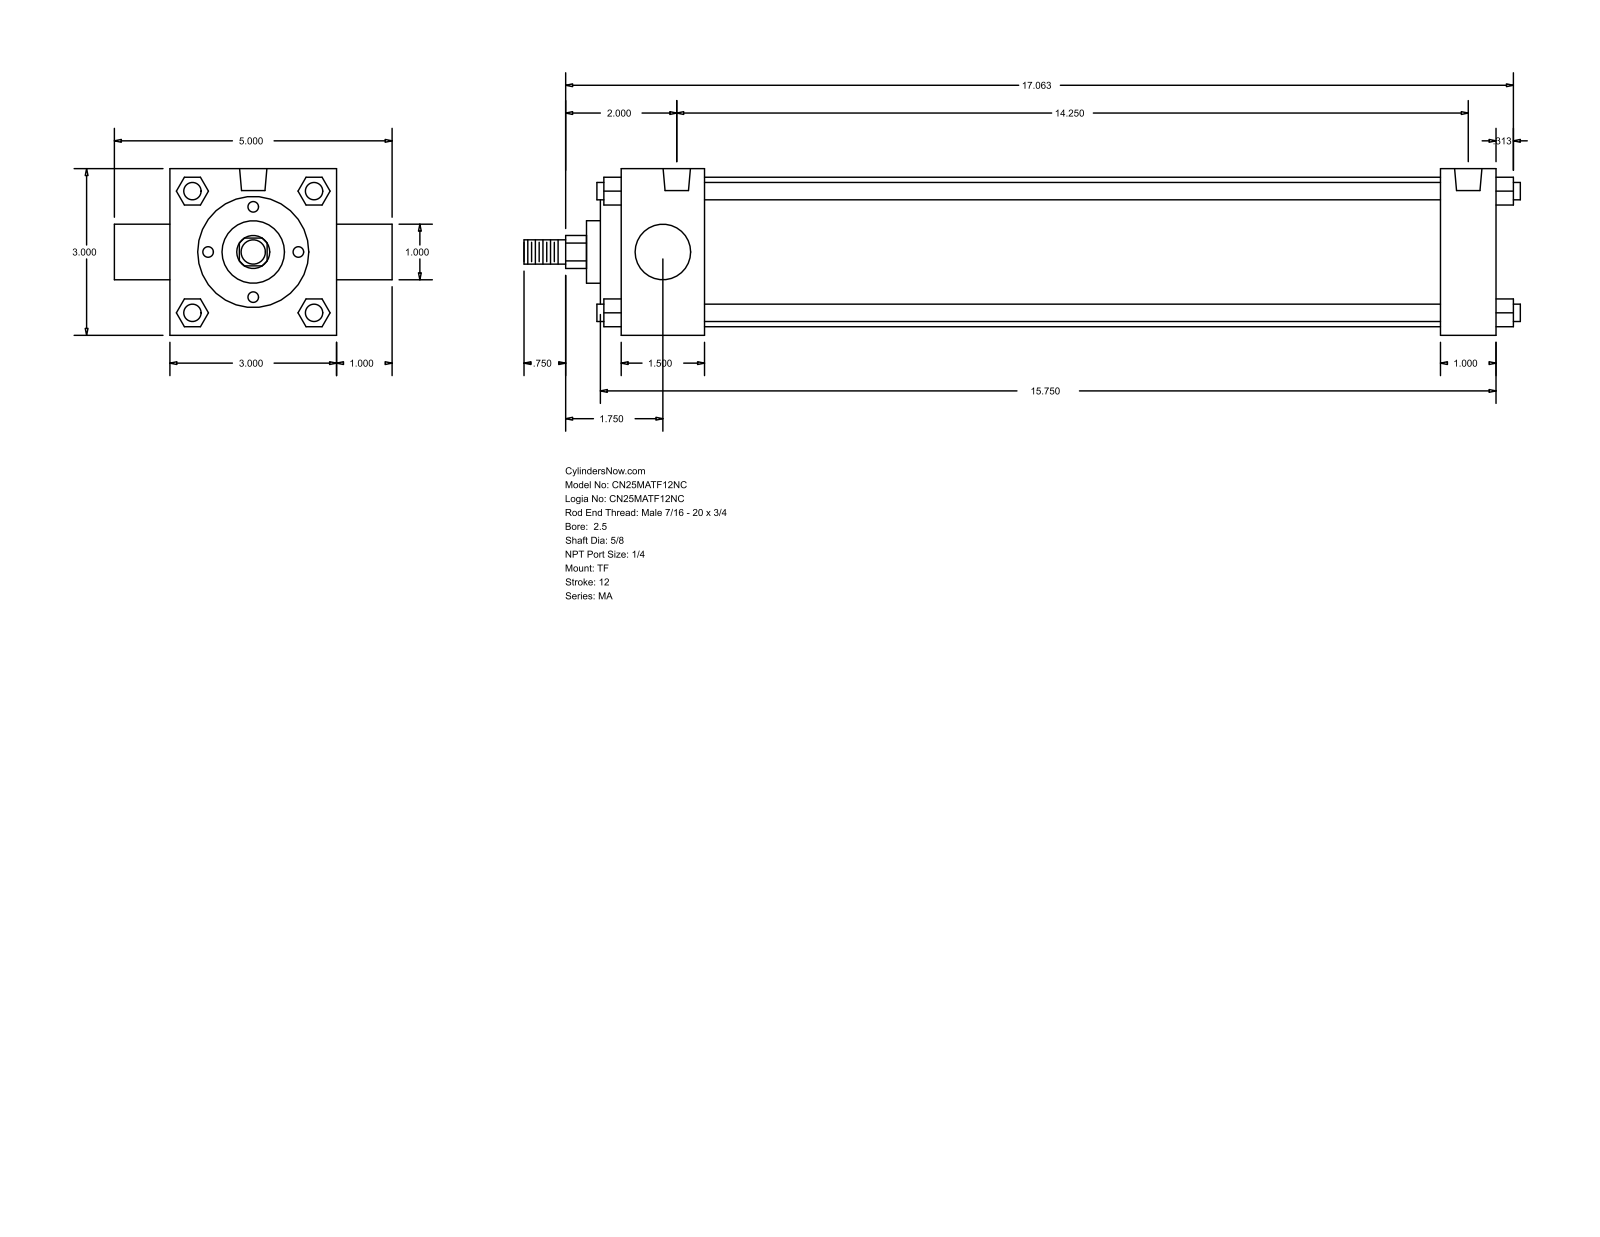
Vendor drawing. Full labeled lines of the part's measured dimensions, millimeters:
Part name (STEP PRODUCT): MA_TF__0250_0.625
STEP written by: GSSL Pune (CONFIG_CONTROL_DESIGN)
Units: millimetres
Bodies: 0 solids, 122 faces (93 planar, 29 cylindrical, 0 other)
Overall size (bounding box): 455.61 × 127 × 76.2
Round holes (diameter × count): ⌀7.94 ×3, ⌀12.49 ×2
Round bosses / shafts (diameter × count): ⌀7.94 ×4, ⌀68.33 ×1, ⌀50.8 ×1, ⌀28.57 ×1, ⌀25.4 ×1, ⌀15.88 ×1, ⌀11.11 ×1
Partial cylindrical surfaces — rounded edges, fillets, slot ends (radius × count): R7.54 ×1
Main face-to-face distances: 76.2, 400.05, 25.4, 38.1, 374.65, 336.55, 361.95, 12.7, 9.52, 47.62
Hole centre spacings: 361.95
